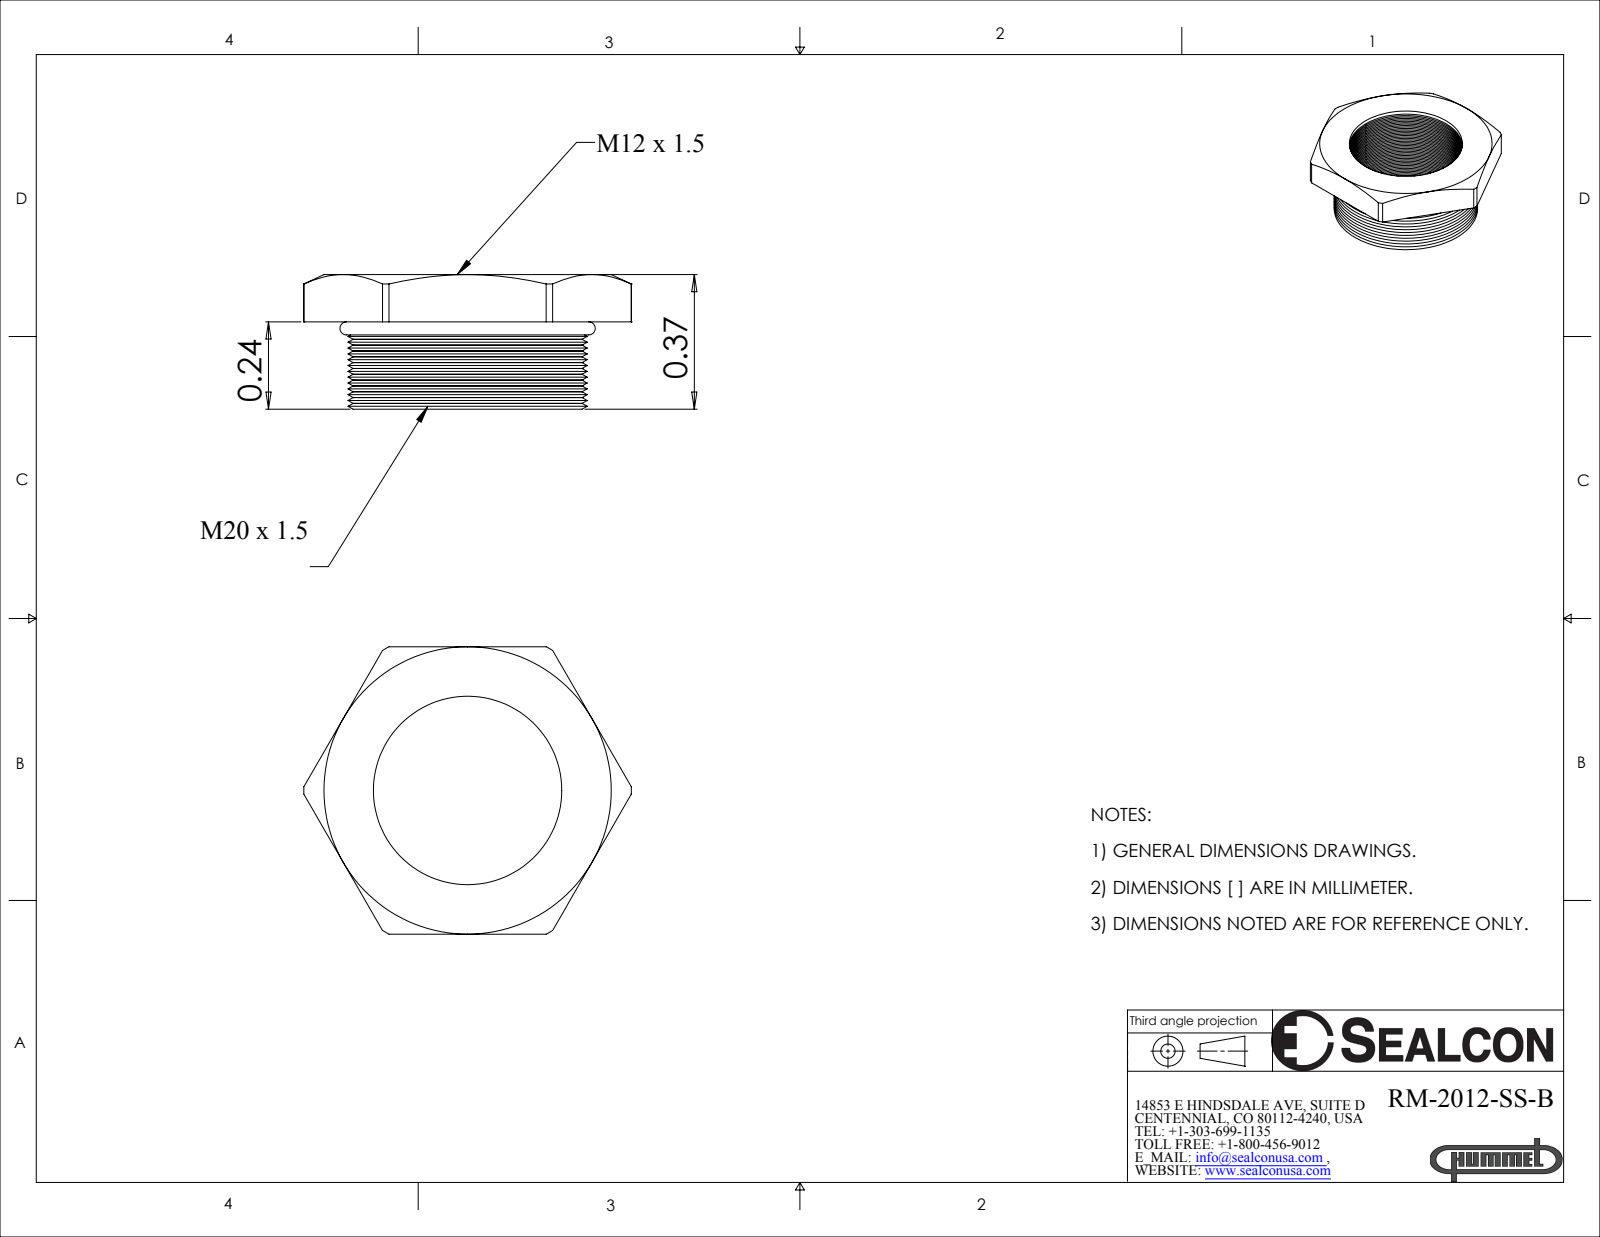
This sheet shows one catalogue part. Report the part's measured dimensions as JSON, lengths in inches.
{"part_name": "RM-2012-SS-B", "step_written_by": "SolidWorks 2008 (CONFIG_CONTROL_DESIGN)", "units": "inches", "bodies": {"solids": 2, "faces": 245, "planar": 9, "cylindrical": 81, "other": 155}, "overall_size": [0.901, 0.79, 0.37], "volume_in3": 0.07, "surface_area_in2": 3.335, "round_holes": [[0.518, 1]], "round_bosses_or_shafts": [[0.63, 1]], "partial_cylinders_radius": [[0.45, 1]], "face_to_face_distances": [0.13, 0.79, 0.24, 0.37]}
